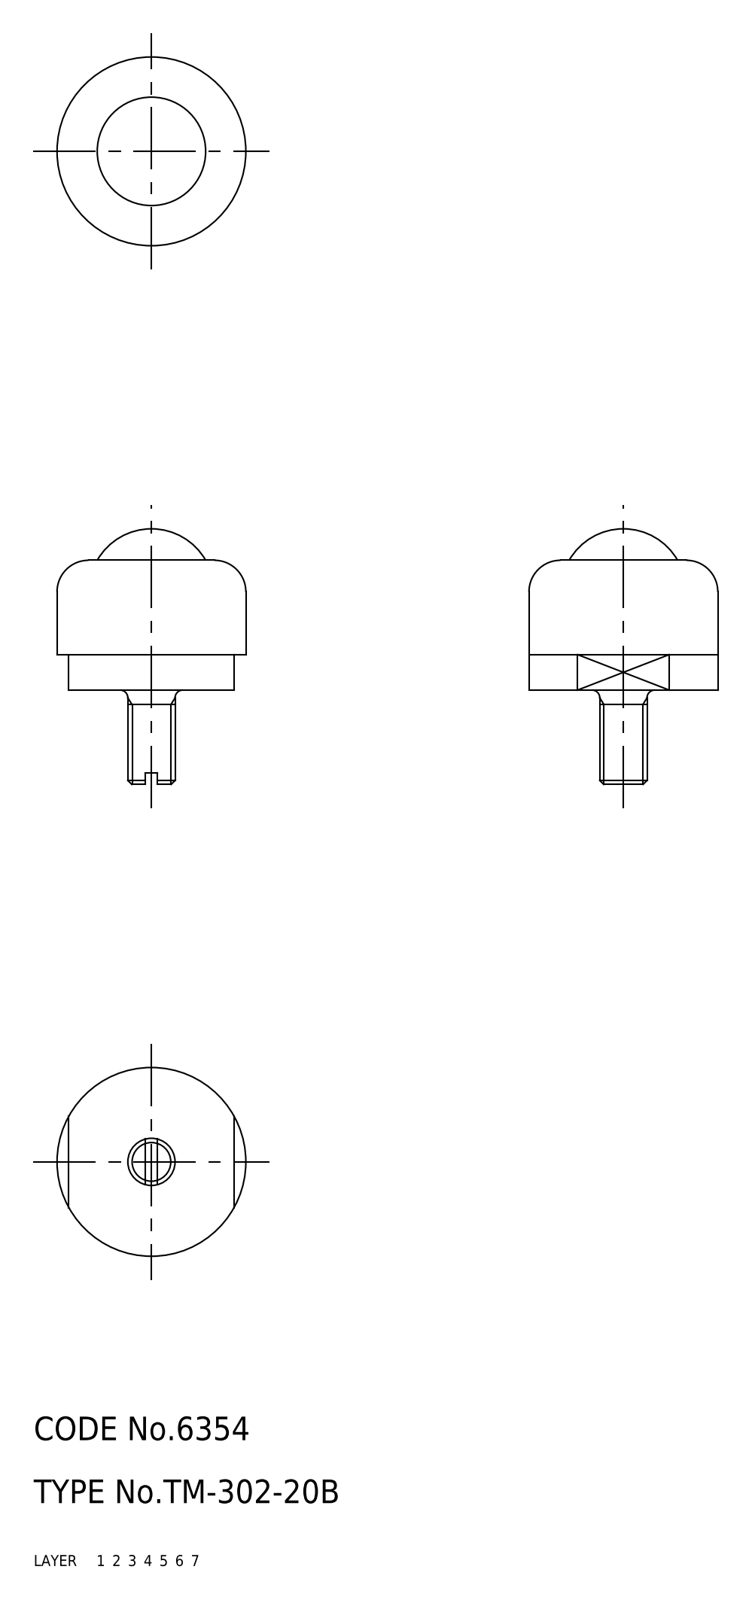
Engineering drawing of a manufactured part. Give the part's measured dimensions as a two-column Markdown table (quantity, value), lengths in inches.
| quantity | value |
| --- | --- |
| part name | 67111084; 67111097; 67111110 |
| STEP written by | CADfix (AUTOMOTIVE_DESIGN) |
| units | inches |
| bodies | 3 solids, 32 faces (0 planar, 0 cylindrical, 32 other) |
| overall size | 1.28 × 0.945 × 0.945 |
| volume | 0.308 in³ |
| surface area | 6.64 in² |
